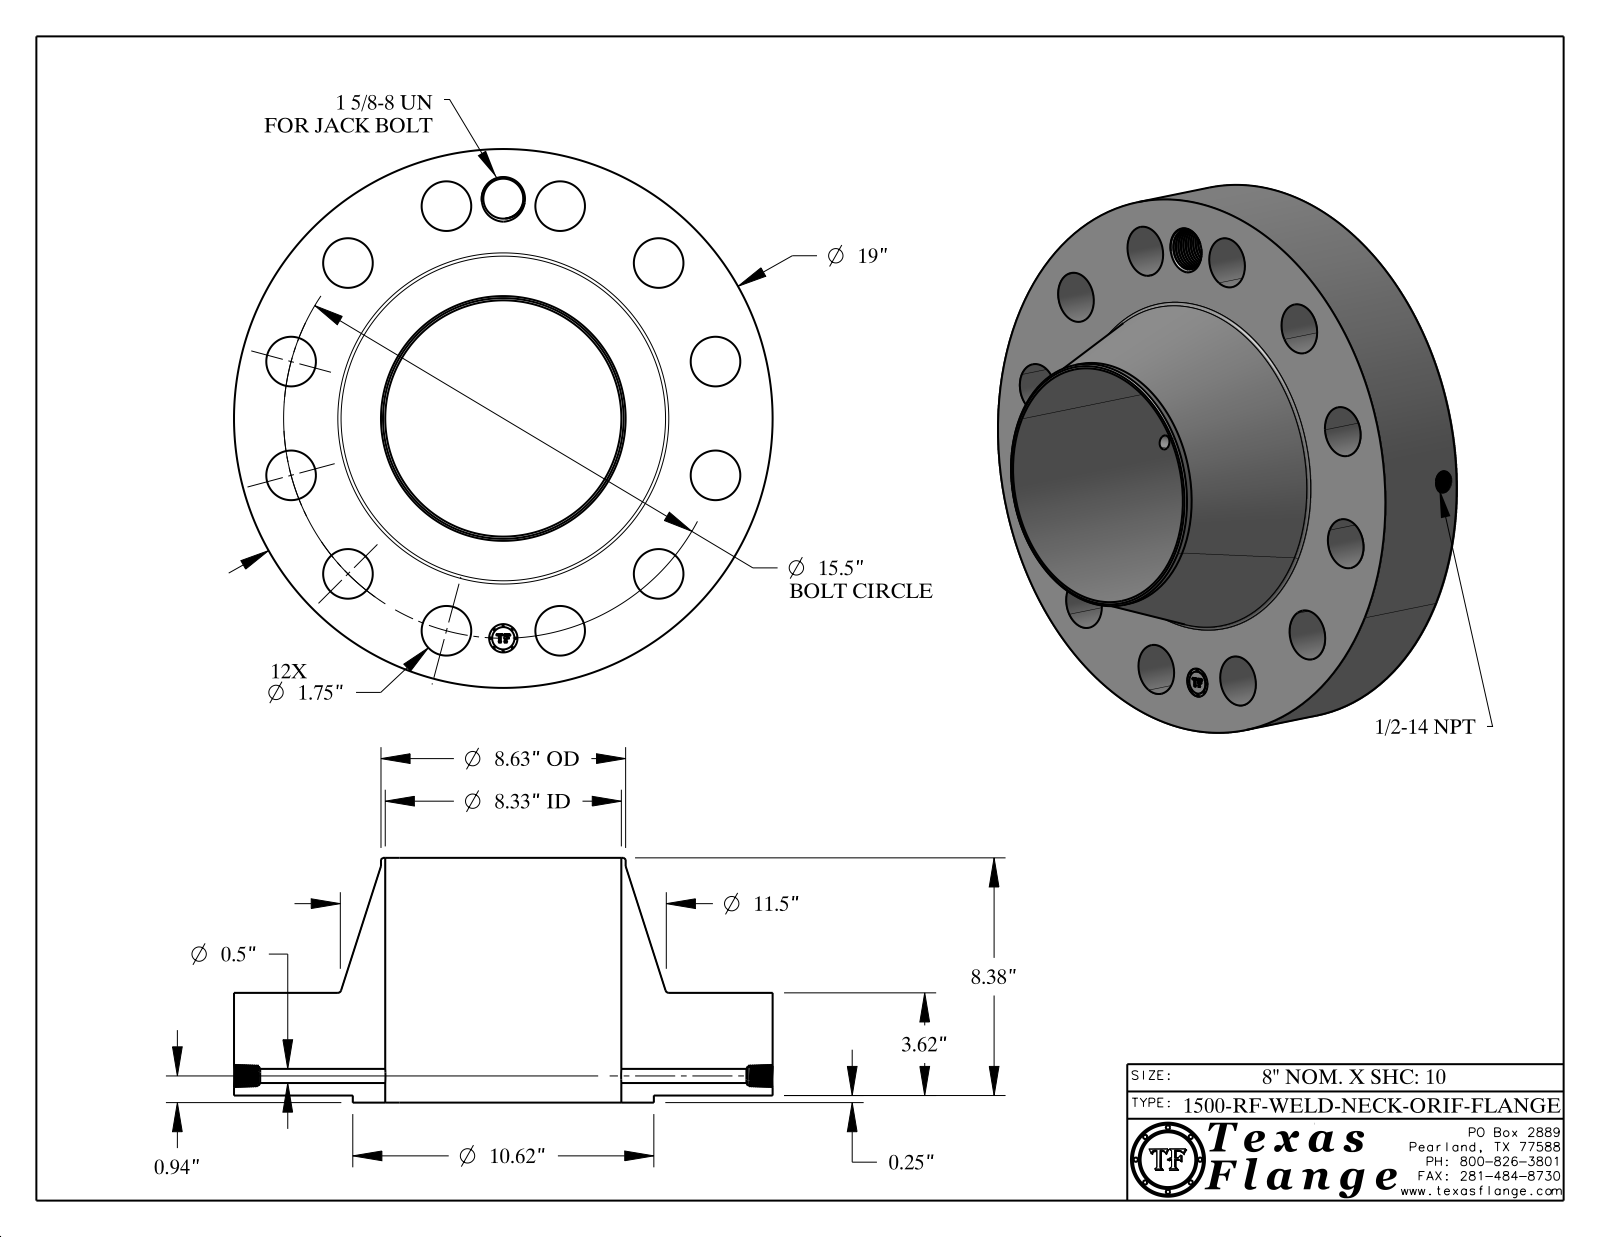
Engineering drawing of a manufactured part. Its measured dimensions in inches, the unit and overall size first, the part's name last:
Units: inches
Overall size (bounding box): 19 × 19 × 8.63
Round holes (diameter × count): ⌀1.75 ×12, ⌀0.5 ×1, ⌀0.672 ×1, ⌀1 ×1, ⌀1.409 ×1, ⌀8.329 ×1
Round bosses / shafts (diameter × count): ⌀0.061 ×8, ⌀19 ×1, ⌀10.62 ×1, ⌀8.63 ×1, ⌀0.788 ×1
Main face-to-face distances: 3.62, 0.25, 3.87, 8.63, 8.38, 4.76, 3.855, 3.605, 0.015, 4.775
Hole centre spacings: 7.75, 13.423, 14.972, 4.011, 7.75, 10.96, 15.5, 2.023
Volume: 839.8 in³ · Surface area: 1 250 in²
Bodies: 1 solid, 861 faces (369 planar, 129 cylindrical, 363 other)
Part name (STEP PRODUCT): 1500-RF-WELD-NECK
STEP written by: CATIA V5 STEP AP214 (AUTOMOTIVE_DESIGN)
